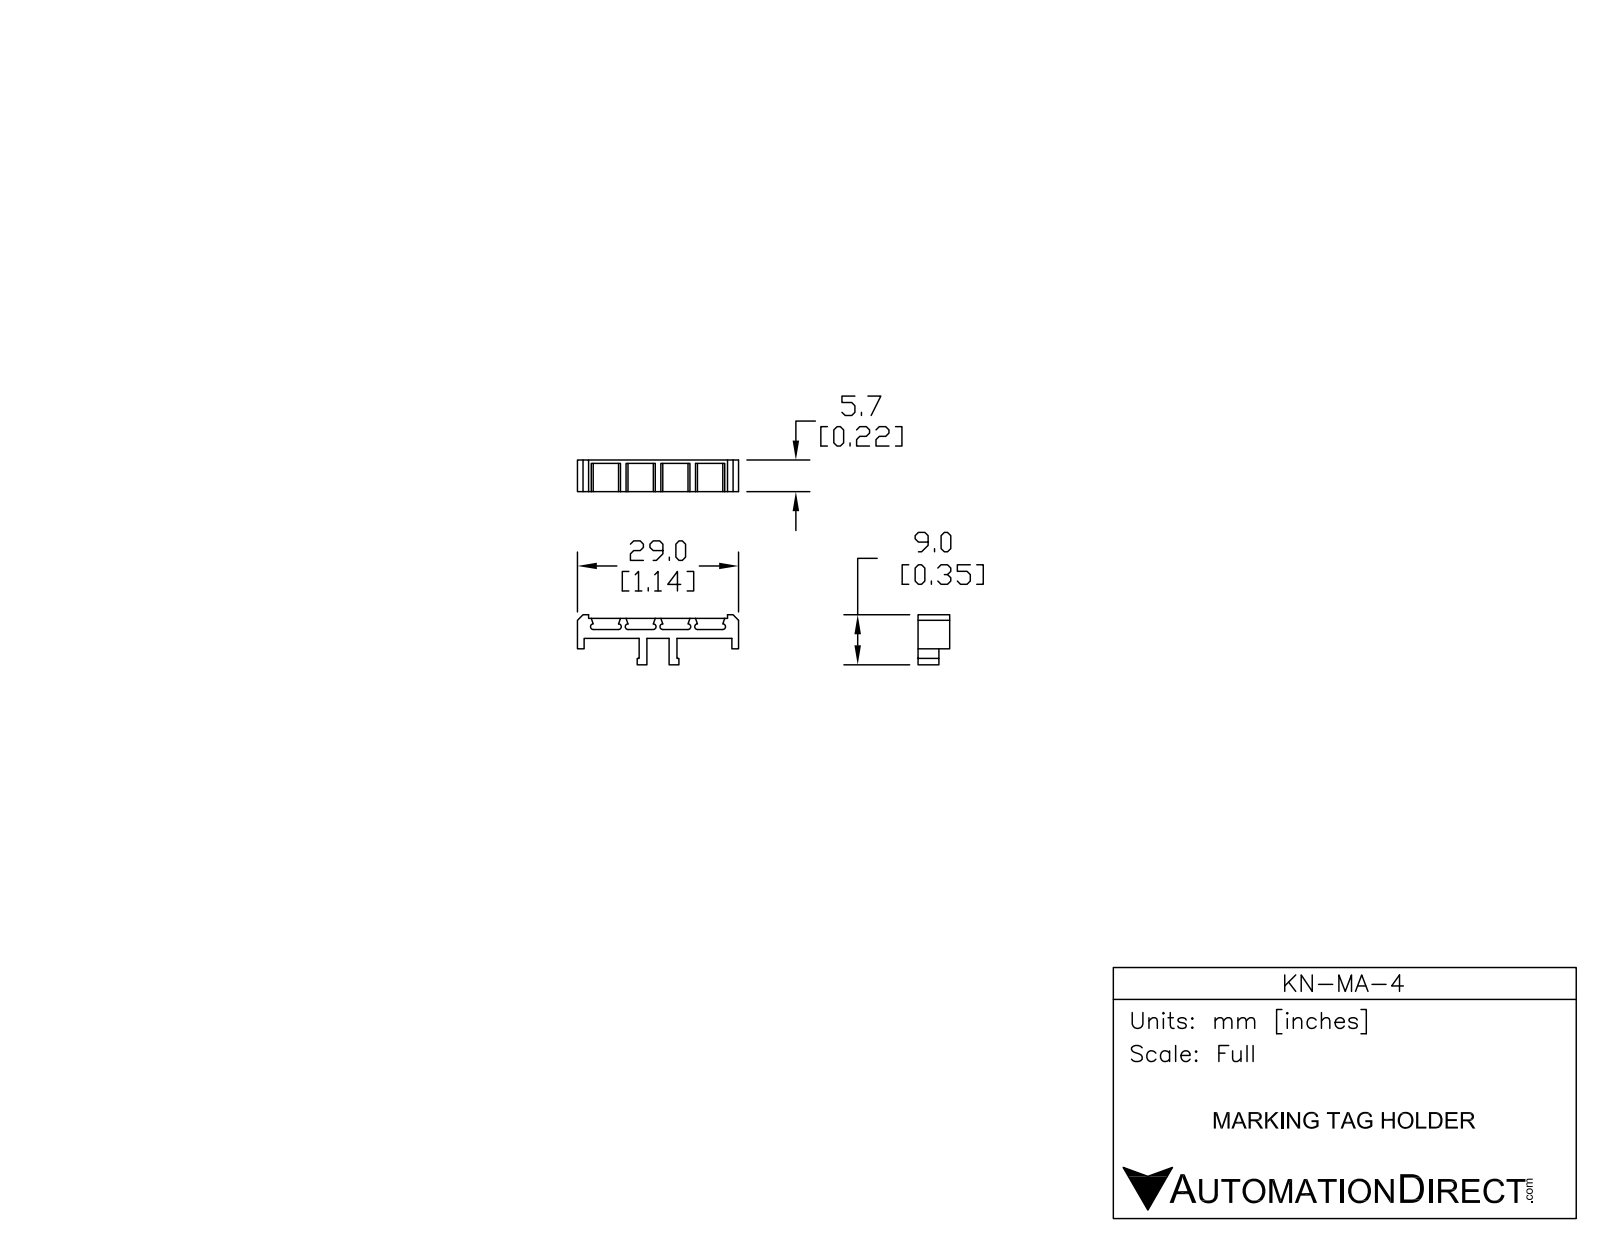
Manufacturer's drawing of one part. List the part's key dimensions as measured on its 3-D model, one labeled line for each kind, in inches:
Part name (STEP PRODUCT): KN-MA-4
STEP written by: SolidWorks 2014 (AUTOMOTIVE_DESIGN)
Units: inches
Bodies: 1 solid, 56 faces (44 planar, 12 cylindrical, 0 other)
Overall size (bounding box): 1.142 × 0.354 × 0.224
Volume: 0.029 in³ · Surface area: 1.3 in²
Partial cylindrical surfaces — rounded edges, fillets, slot ends (radius × count): R0.02 ×8
Main face-to-face distances: 0.063, 0.224, 0.079, 0.024, 0.201, 0.492, 0.65, 0.142, 0.232, 1.142
